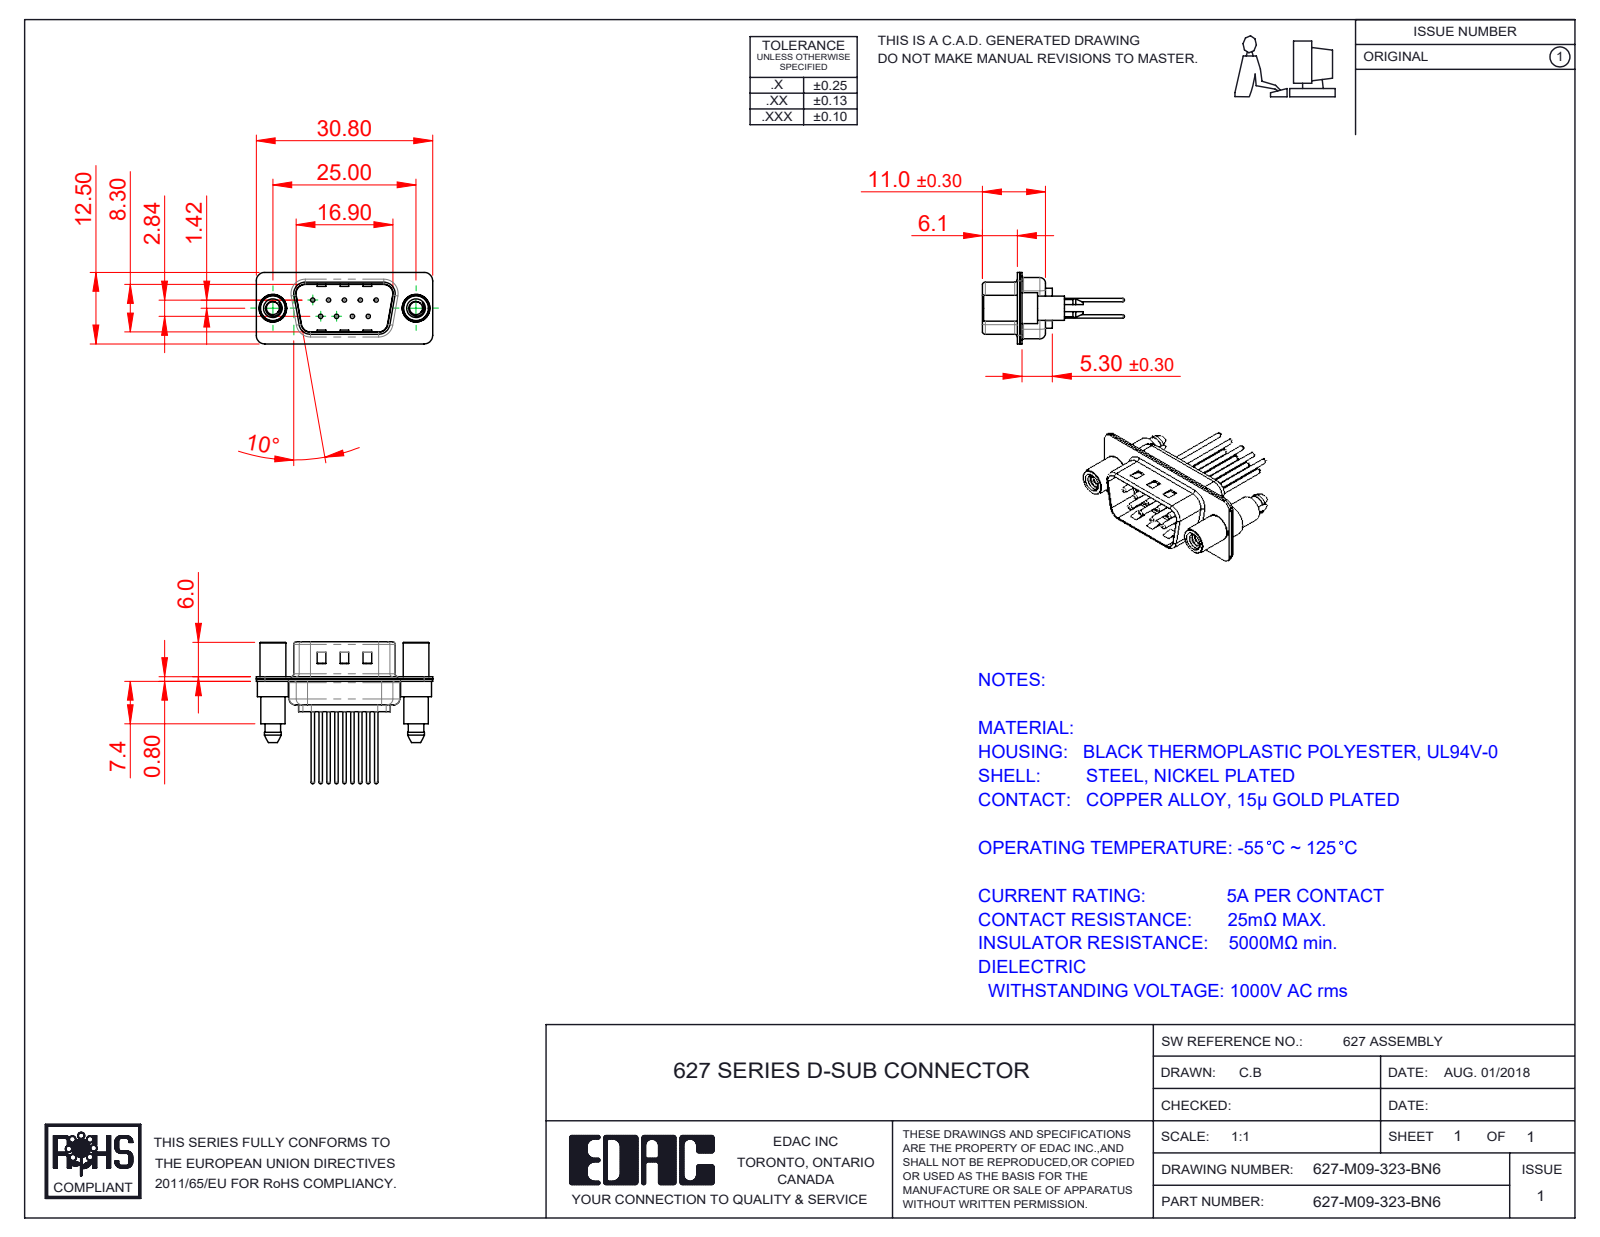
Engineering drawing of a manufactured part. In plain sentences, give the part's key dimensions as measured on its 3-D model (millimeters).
The part is named "627M Housing_09 Contacts; 627M 4-40 Threaded Standoff and Boardlock; 627M Shell Front_09 Contacts; 627M Shell Rear_09 Contacts (+3 more)". Its 3-D file was written by "SolidWorks 2020 (CONFIG_CONTROL_DESIGN)". It is 14 solids with 689 faces: 188 planar, 283 cylindrical and 218 other. Overall it measures 30.8 by 24.77 by 12.5 millimeters. Its volume is 1 666 cubic millimeters and its surface area 4 158 square millimeters. Round holes: 9 of diameter 0.75, 9 of diameter 1.6, 9 of diameter 2, 2 of diameter 2.26, 2 of diameter 4, 2 of diameter 4.8. Round bosses or shafts: 9 of diameter 1.5, 9 of diameter 0.6, 2 of diameter 5.4, 2 of diameter 4.9, 2 of diameter 4.5, 2 of diameter 4.25. Partial cylindrical surfaces (rounded edges, fillets, slot ends): 18 of radius 1.5, 12 of radius 2, 10 of radius 1.6, 8 of radius 0.5, 4 of radius 0.25, 4 of radius 0.6, 4 of radius 0.65, 4 of radius 0.9. The main face-to-face distances are 0.4, 0.8, 9.5, 9.1, 8.7, 0.65, 9.9, 1.2, 5.3, 6.1. The hole center spacings are 3.16, 2.77, 5.54, 5.03, 5.04, 8.31, 7.1, 7.48.
